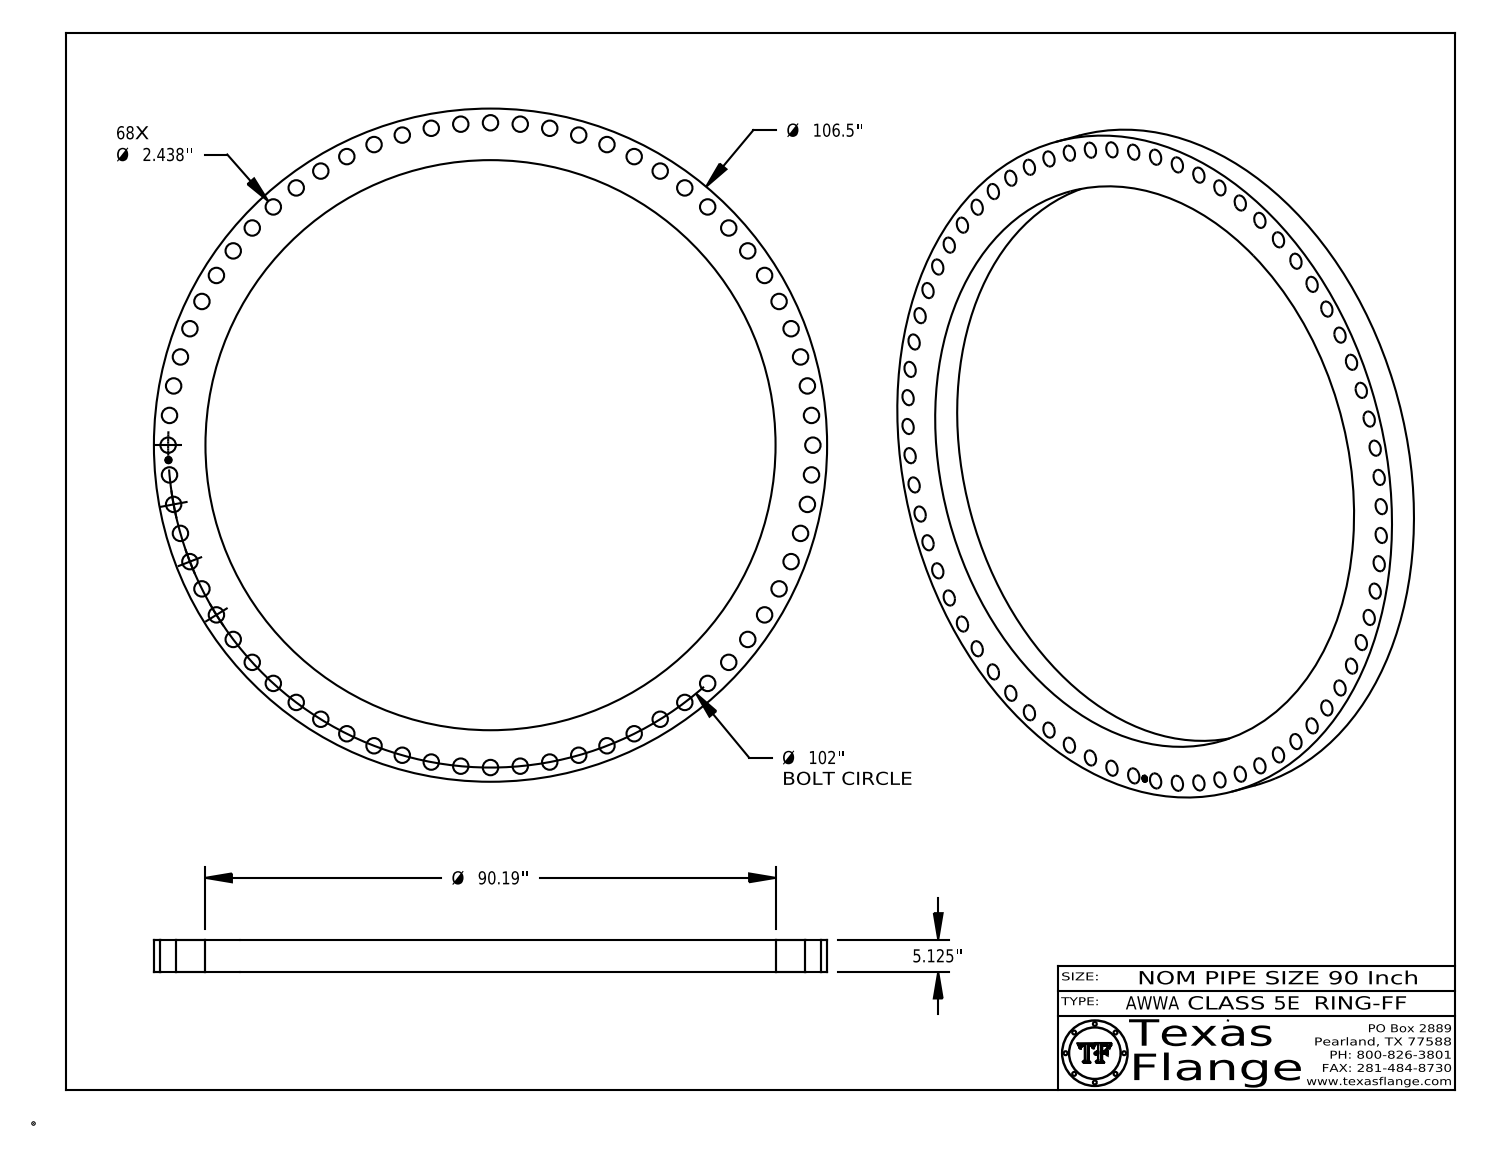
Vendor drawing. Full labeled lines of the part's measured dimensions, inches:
Part name (STEP PRODUCT): AWWA Class 5E-RING-FF
STEP written by: CATIA V5 STEP AP214 (AUTOMOTIVE_DESIGN)
Units: inches
Bodies: 1 solid, 527 faces (367 planar, 160 cylindrical, 0 other)
Overall size (bounding box): 106.5 × 106.5 × 5.125
Volume: 11 286 in³ · Surface area: 10 241 in²
Round holes (diameter × count): ⌀2.438 ×68, ⌀1 ×1, ⌀90.19 ×1
Round bosses / shafts (diameter × count): ⌀0.061 ×8, ⌀106.5 ×1, ⌀0.788 ×1
Main face-to-face distances: 5.125, 5.11, 0.015, 0.019, 0.298, 0.292, 0.054, 0.194, 0.248, 0.044
Hole centre spacings: 51, 9.411, 18.743, 4.711, 23.353, 14.092, 32.415, 41.2
